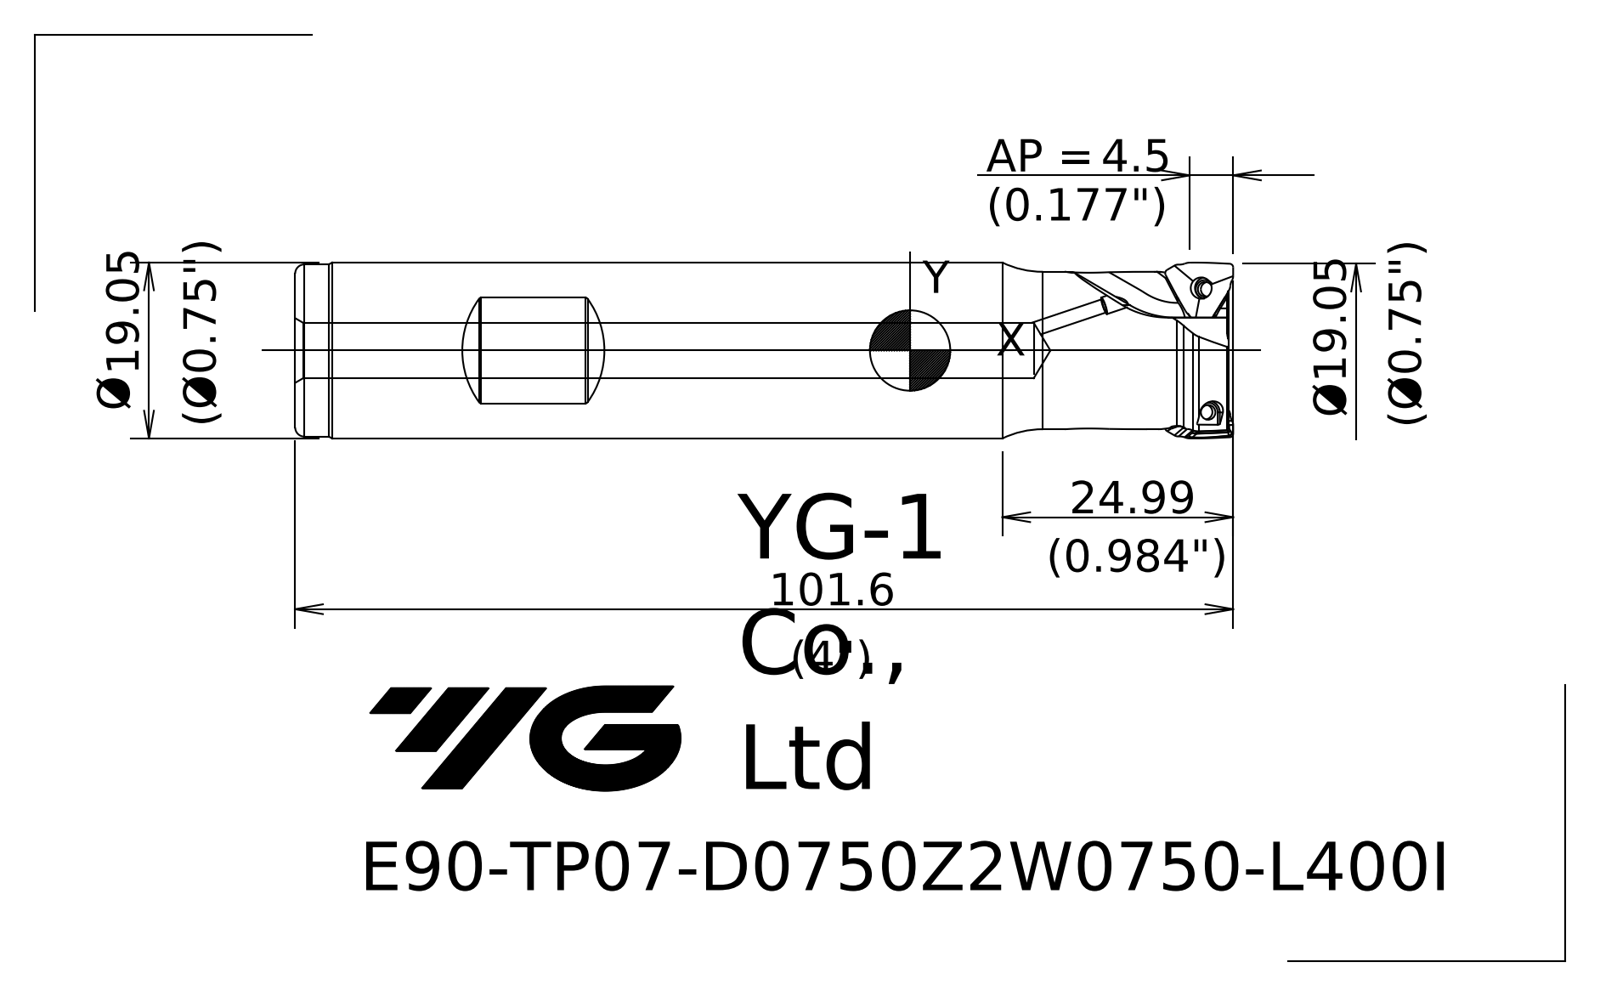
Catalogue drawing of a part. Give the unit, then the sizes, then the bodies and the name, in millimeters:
Units: millimetres
Overall size (bounding box): 101.6 × 19.09 × 19.09
Round holes (diameter × count): ⌀1.5 ×1, ⌀6 ×1
Round bosses / shafts (diameter × count): ⌀19.05 ×1, ⌀18.65 ×1, ⌀17.05 ×1
Partial cylindrical surfaces — rounded edges, fillets, slot ends (radius × count): R0.3 ×2
Main face-to-face distances: 100.95, 101.1
Volume: 25 020 mm³ · Surface area: 8 902 mm²
Bodies: 1 solid, 48 faces (6 planar, 7 cylindrical, 35 other)
Part name (STEP PRODUCT): 102255F02B59yk8c
STEP written by: SIEMENS PLM Software NX 10.0 (AP203_CONFIGURATION_CONTROLLED_3D_DESIGN_OF_MECHANICAL_PARTS_AND_ASSEMBLIES_MIM_LF)
